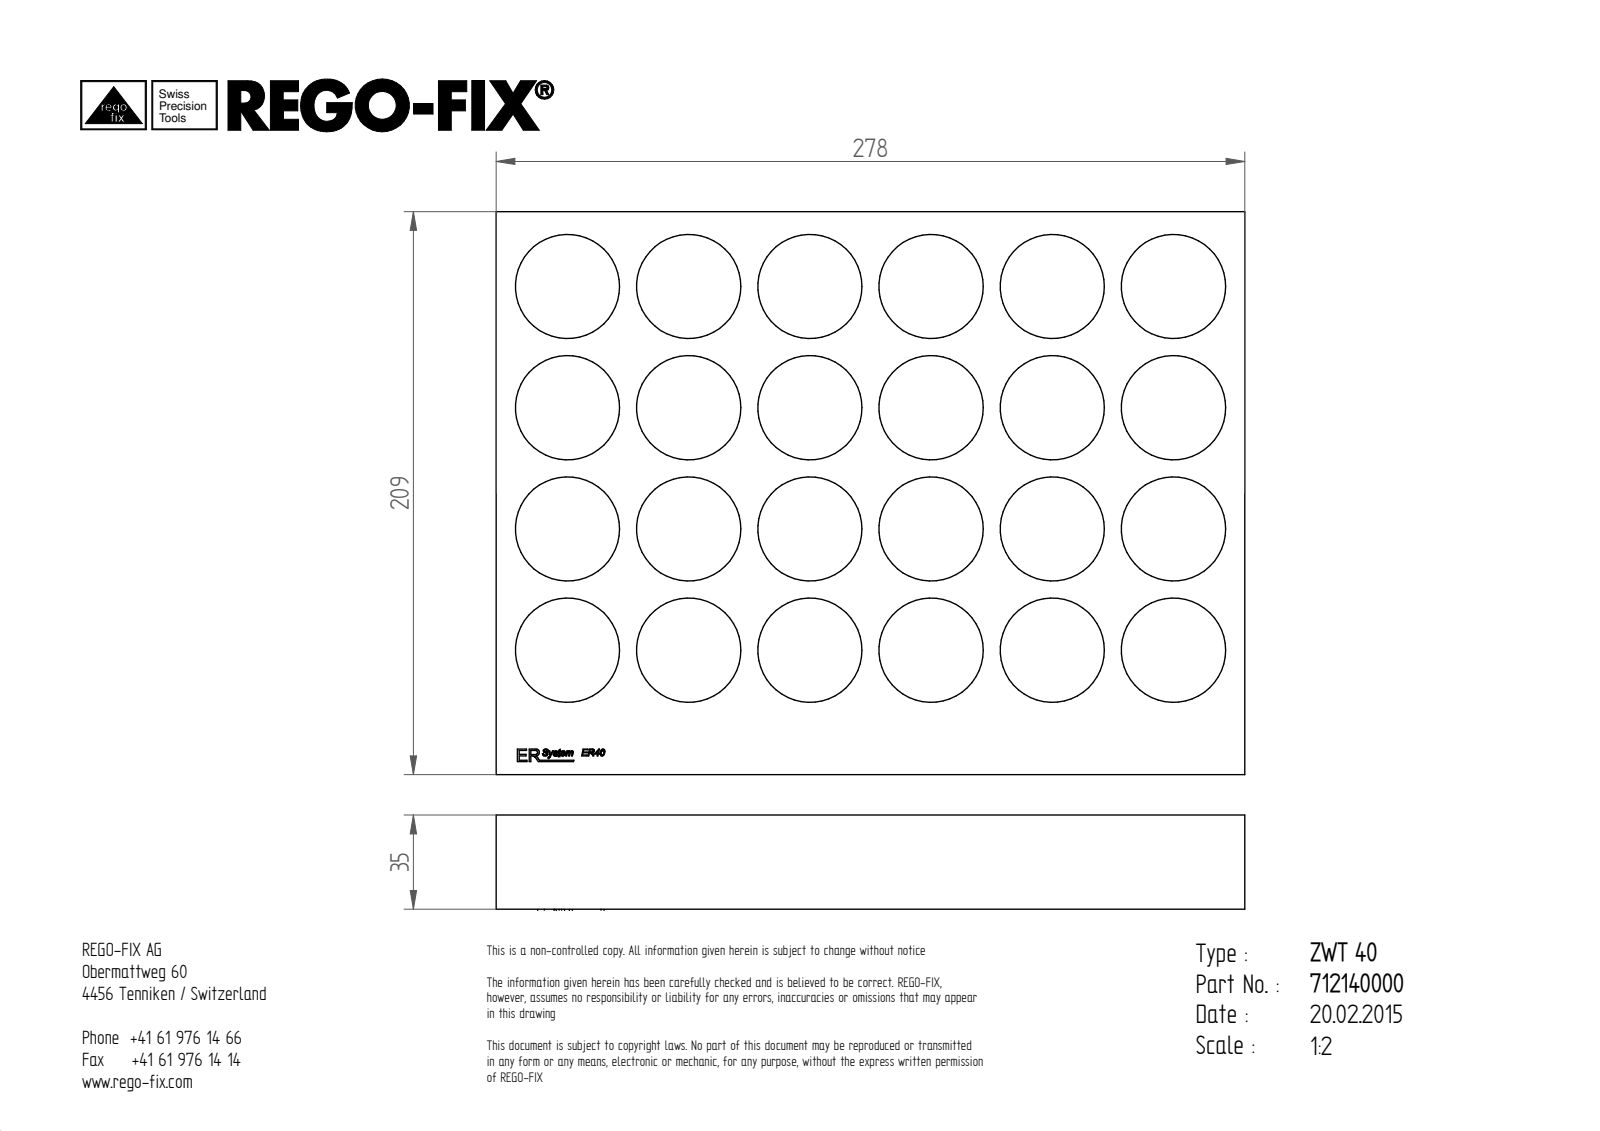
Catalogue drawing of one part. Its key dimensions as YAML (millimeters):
step_written_by: "Unknown (AUTOMOTIVE_DESIGN)"
units: millimeters
bodies: {solids: 1, faces: 175, planar: 125, cylindrical: 24, other: 26}
overall_size: [278, 209, 35]
volume: 1300000
surface_area: 226179
round_holes:
  - {diameter: 38.7, count: 24}
face_to_face_distances: [35, 9, 26, 209, 278, 34.9, 25.9, 4.83, 204.17, 0.5]
hole_center_spacings: [100.62, 45, 63.64, 90, 142.3, 162.25, 135, 127.28]
